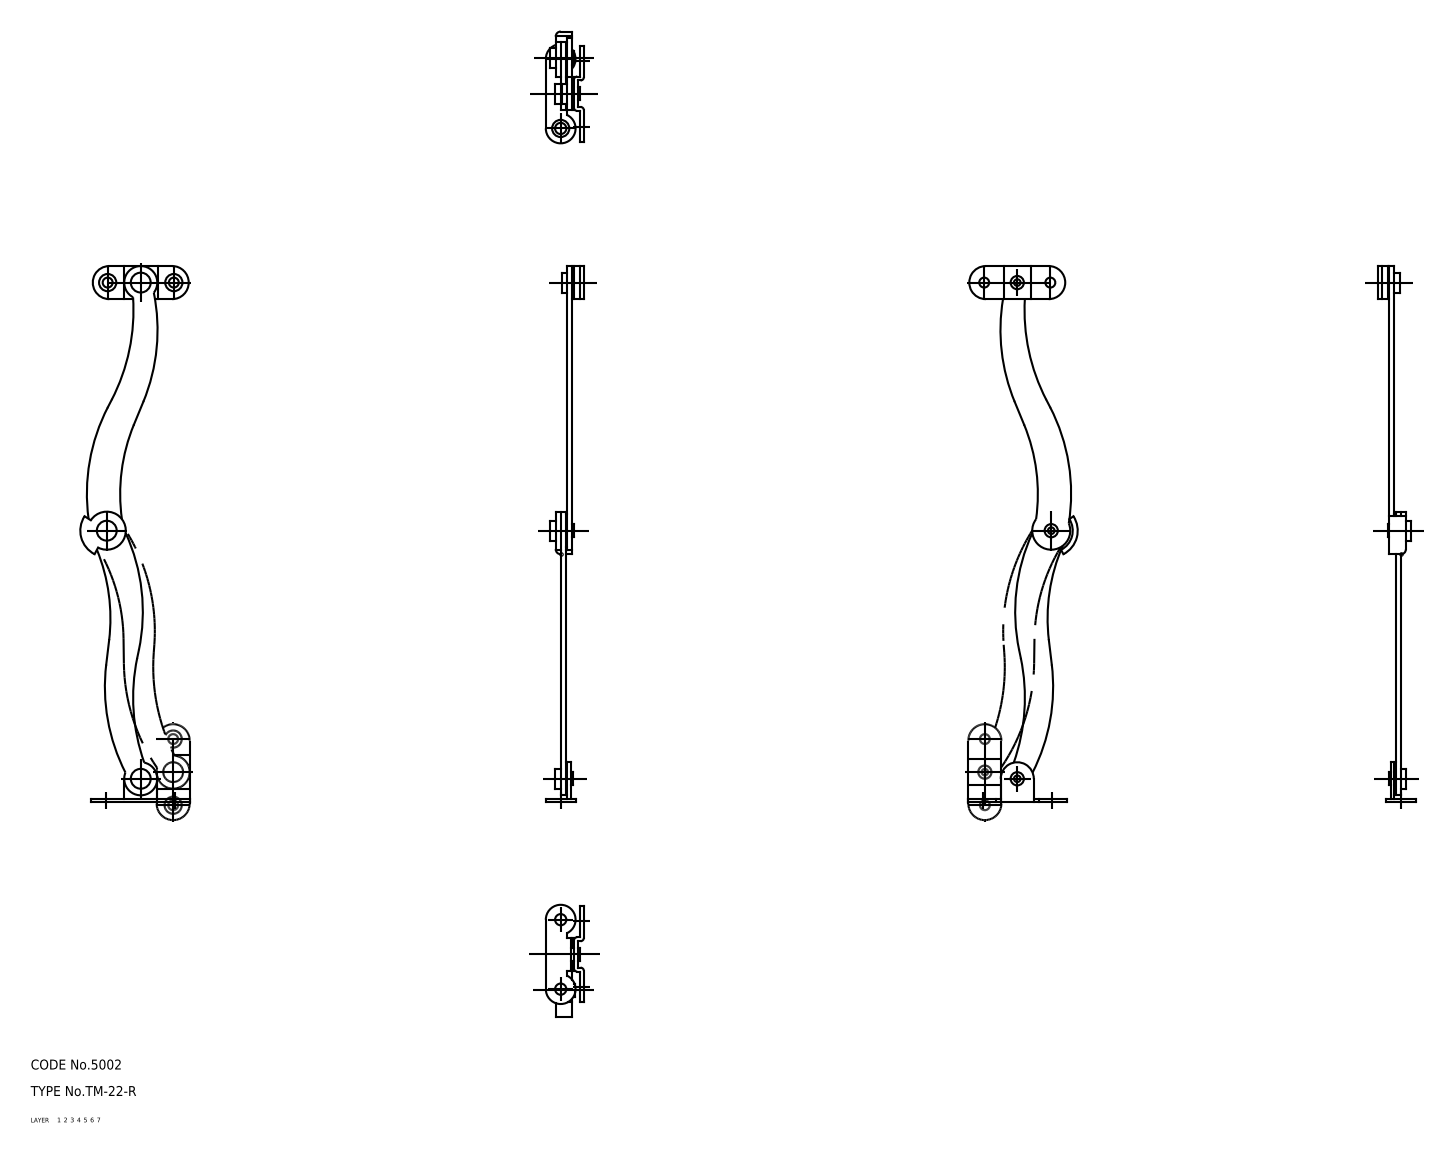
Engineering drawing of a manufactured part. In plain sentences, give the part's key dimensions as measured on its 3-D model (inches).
The part is named "rivet_3_mr; rivet_1_mr; rivet_2_mr; washer_mr-2 (+8 more)". Its 3-D file was written by "CADfix (AUTOMOTIVE_DESIGN)". It is 11 solids with 138 faces: 0 planar, 0 cylindrical and 138 other. Overall it measures 6.378 by 1.31 by 0.453 inches. Its volume is 0.214 cubic inches and its surface area 9.925 square inches.
